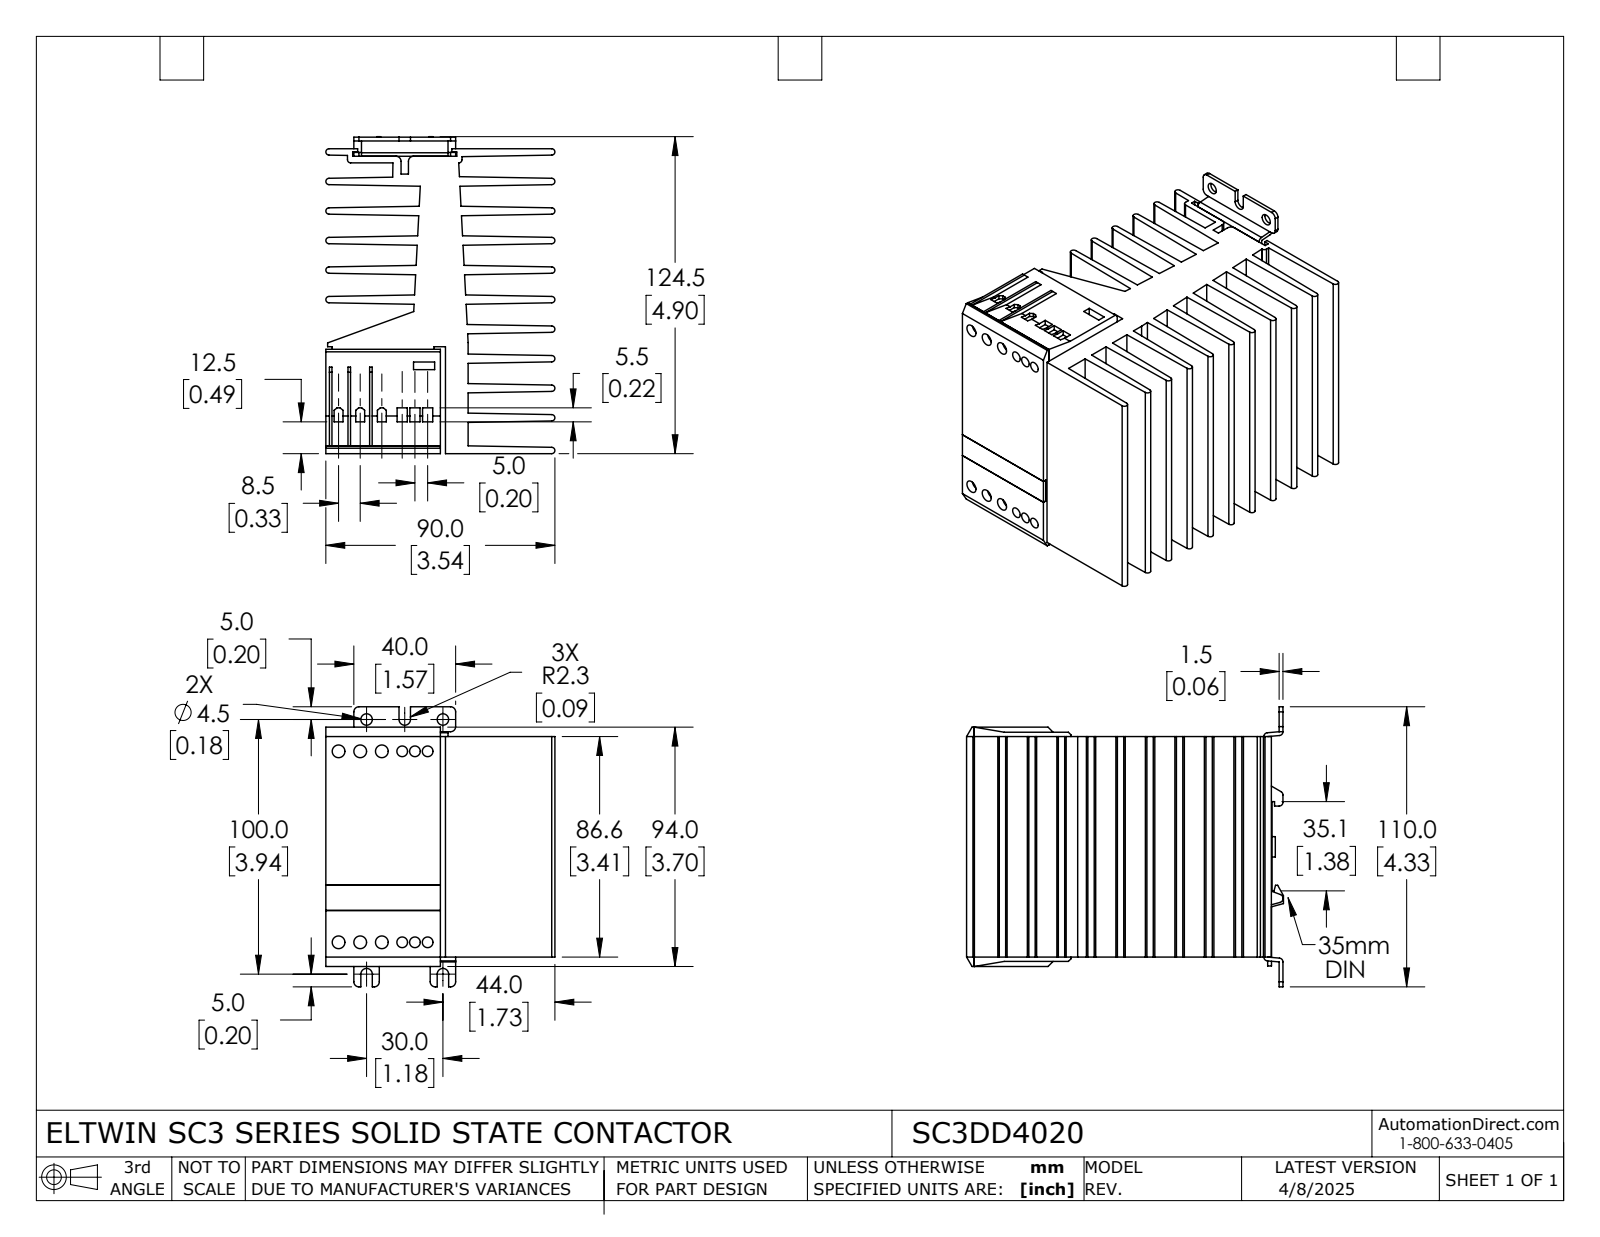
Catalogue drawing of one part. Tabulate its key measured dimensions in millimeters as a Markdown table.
| quantity | value |
| --- | --- |
| part name | SC3DD4020 |
| STEP written by | SolidWorks 2021 (AUTOMOTIVE_DESIGN) |
| units | millimeters |
| bodies | 5 solids, 440 faces (326 planar, 114 cylindrical, 0 other) |
| overall size | 124.5 × 110 × 90 |
| volume | 511 300 mm³ |
| surface area | 179 300 mm² |
| round holes (diameter × count) | 4.2 × 6, 4.4 × 6, 5 × 6, 6 × 6, 4.5 × 2 |
| round bosses / shafts (diameter × count) | 8 × 1 |
| partial cylindrical surfaces (radius × count) | 1.2 × 19, 2 × 18, 1.5 × 10, 1.3 × 4, 2.3 × 3 |
| main face-to-face distances | 11.6, 23.2, 34.8, 4, 7.6, 4, 46.4, 42.4, 46.4, 54 |
| hole center spacings | 75, 5, 8.5, 75.2, 75.5, 30, 8, 10 |
